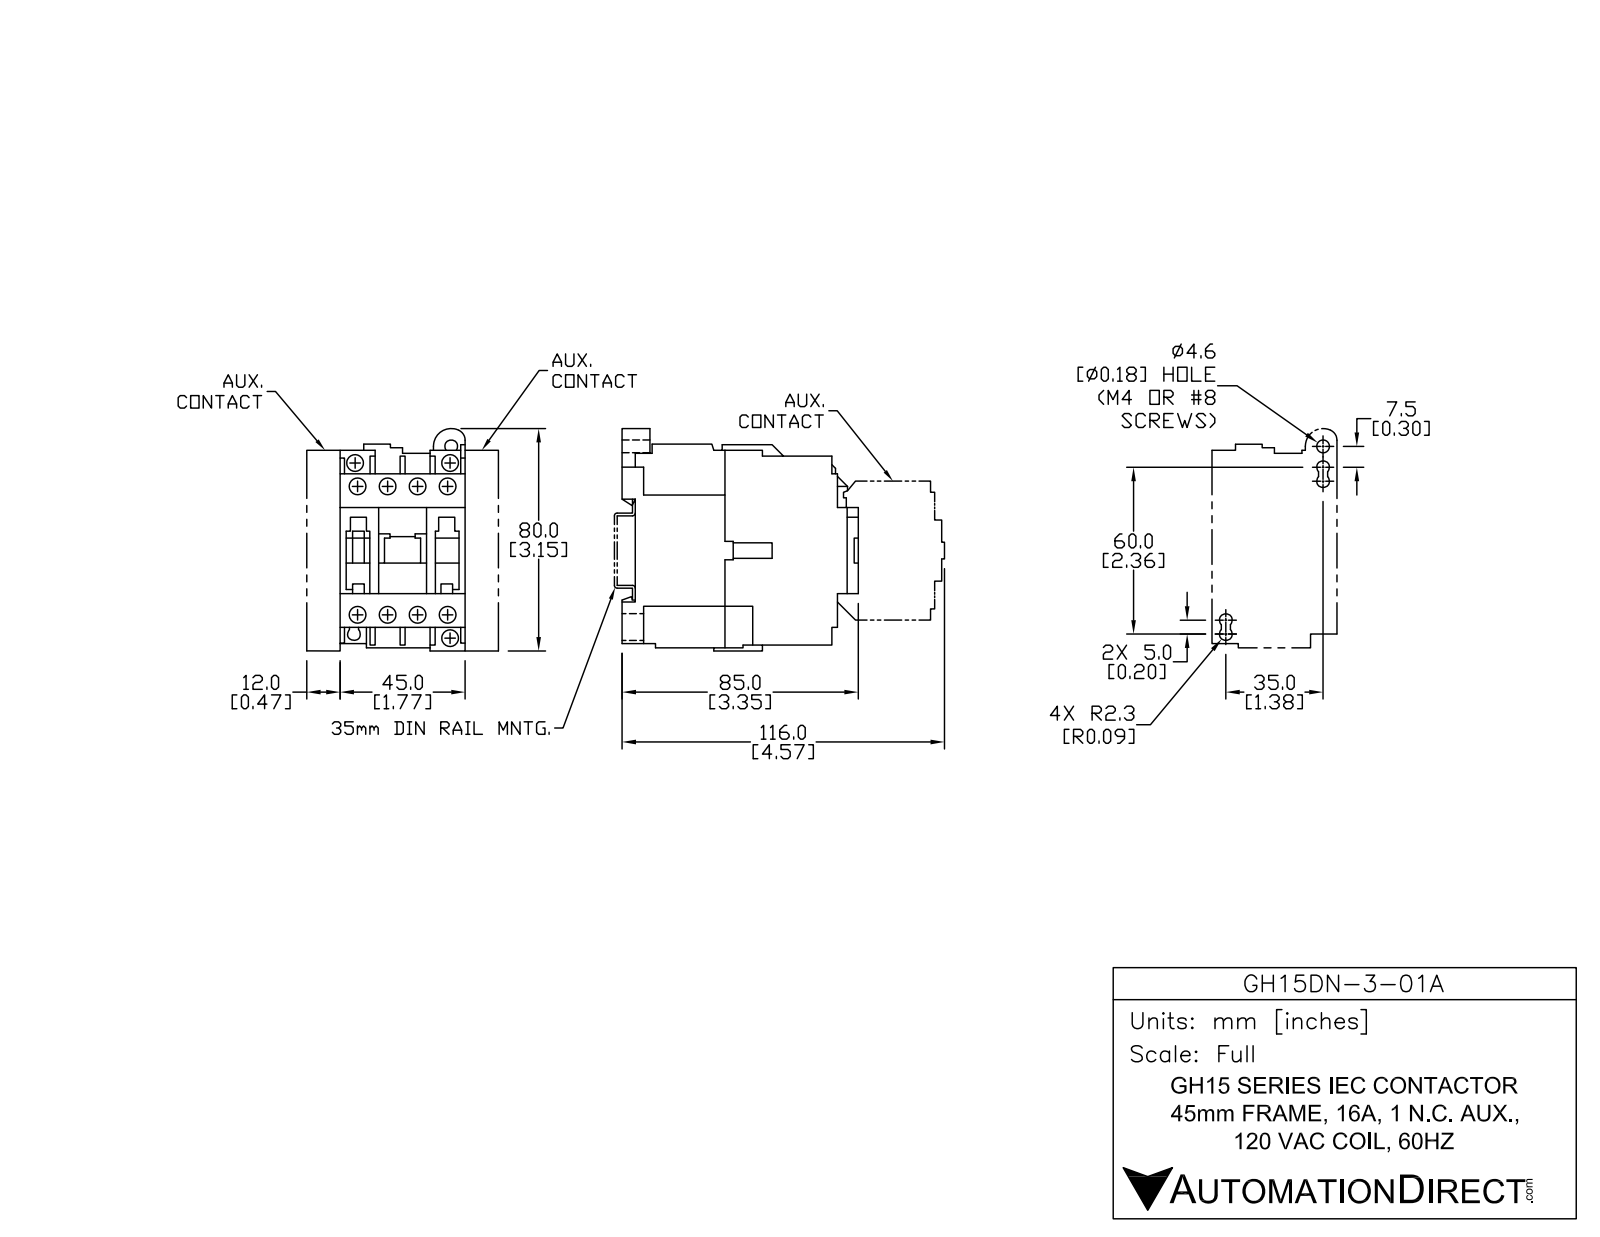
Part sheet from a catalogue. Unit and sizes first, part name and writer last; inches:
Units: inches
Overall size (bounding box): 3.366 × 3.15 × 1.772
Round holes (diameter × count): ⌀0.246 ×9, ⌀0.256 ×2, ⌀0.181 ×1
Partial cylindrical surfaces — rounded edges, fillets, slot ends (radius × count): R0.039 ×10, R0.091 ×8, R0.187 ×8, R0.118 ×2, R0.196 ×1, R0.197 ×1
Main face-to-face distances: 1.772, 0.374, 1.398, 0.477, 0.92, 0.315, 0.276, 1.329, 0.409, 1.294
Hole centre spacings: 0.443, 1.855, 0.886, 1.802, 2.007, 0.3, 1.329, 2.102
Volume: 11.98 in³ · Surface area: 55.48 in²
Bodies: 1 solid, 666 faces (447 planar, 65 cylindrical, 154 other)
Part name (STEP PRODUCT): GH15DN-3-01A
STEP written by: SolidWorks 2009 (AUTOMOTIVE_DESIGN)
